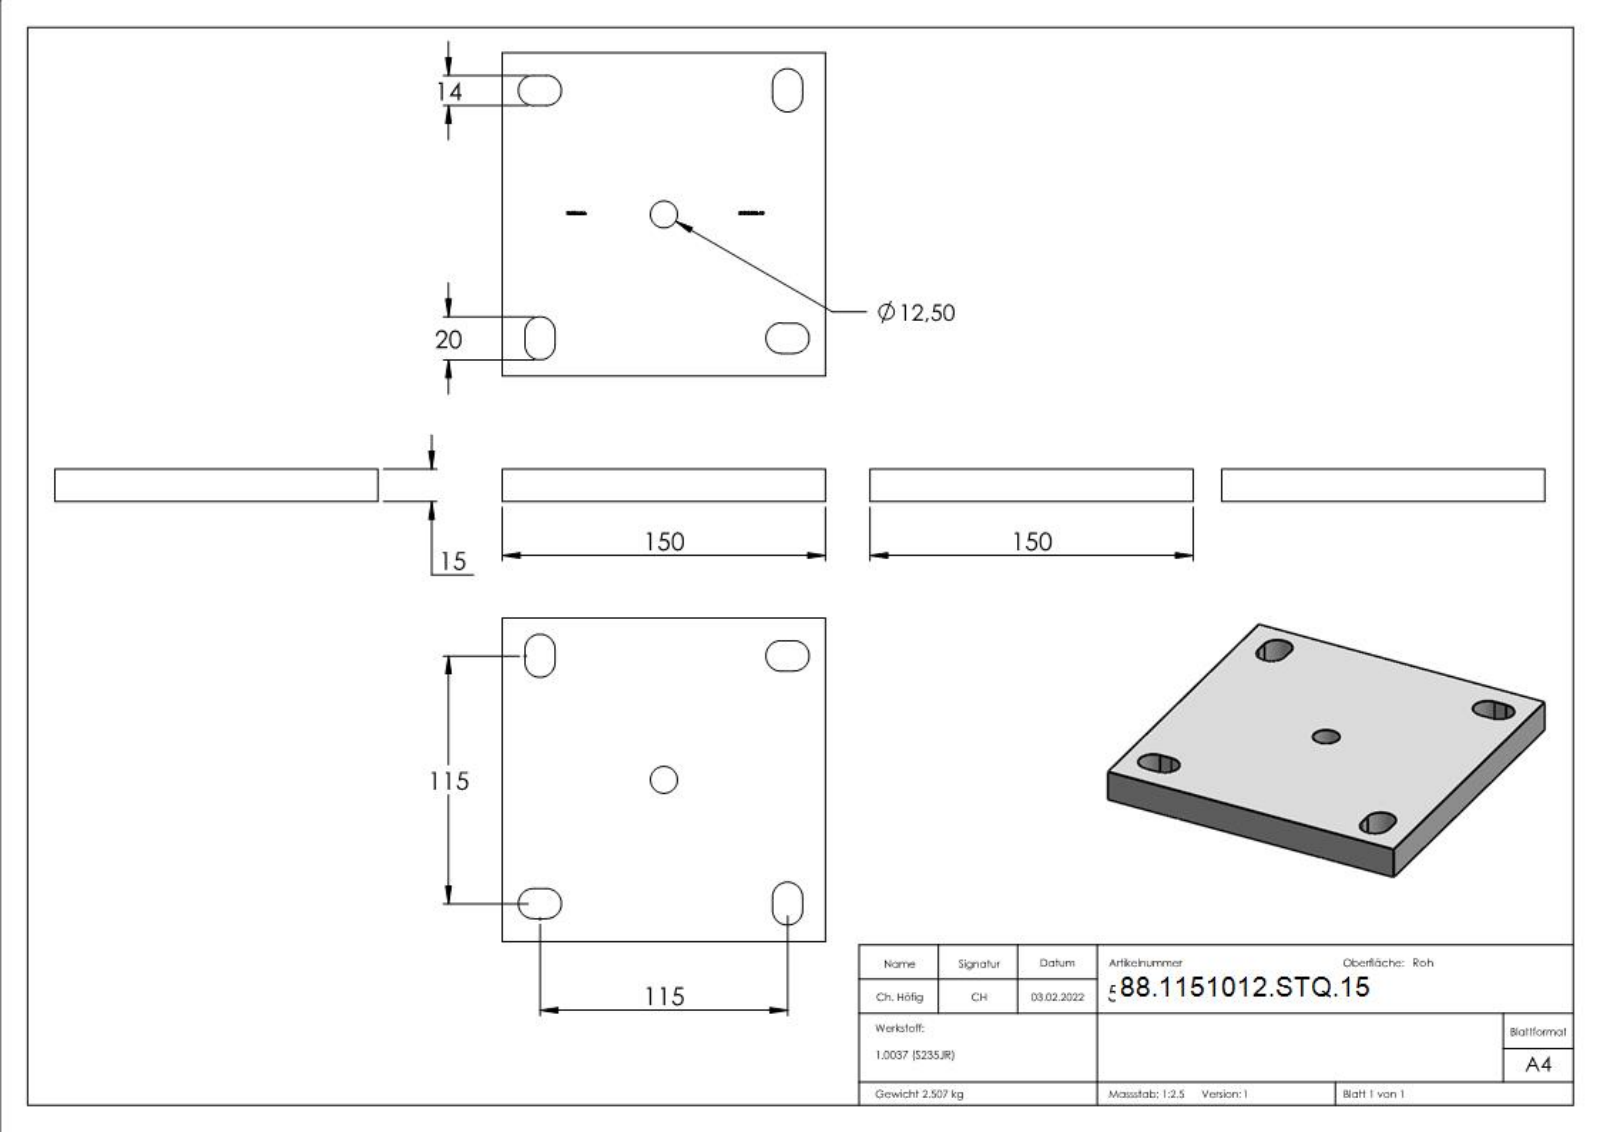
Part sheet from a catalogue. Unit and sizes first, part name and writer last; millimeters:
Units: millimetres
Overall size (bounding box): 150 × 150 × 15
Round holes (diameter × count): ⌀12.5 ×1
Partial cylindrical surfaces — rounded edges, fillets, slot ends (radius × count): R7 ×8
Main face-to-face distances: 15, 150, 10.5, 24.5, 125.5, 139.5, 14, 115, 129, 101
Volume: 321 382 mm³ · Surface area: 55 809 mm²
Bodies: 1 solid, 269 faces (153 planar, 12 cylindrical, 104 other)
Part name (STEP PRODUCT): 51012-STQ-15
STEP written by: SolidWorks 2018 (CONFIG_CONTROL_DESIGN)
